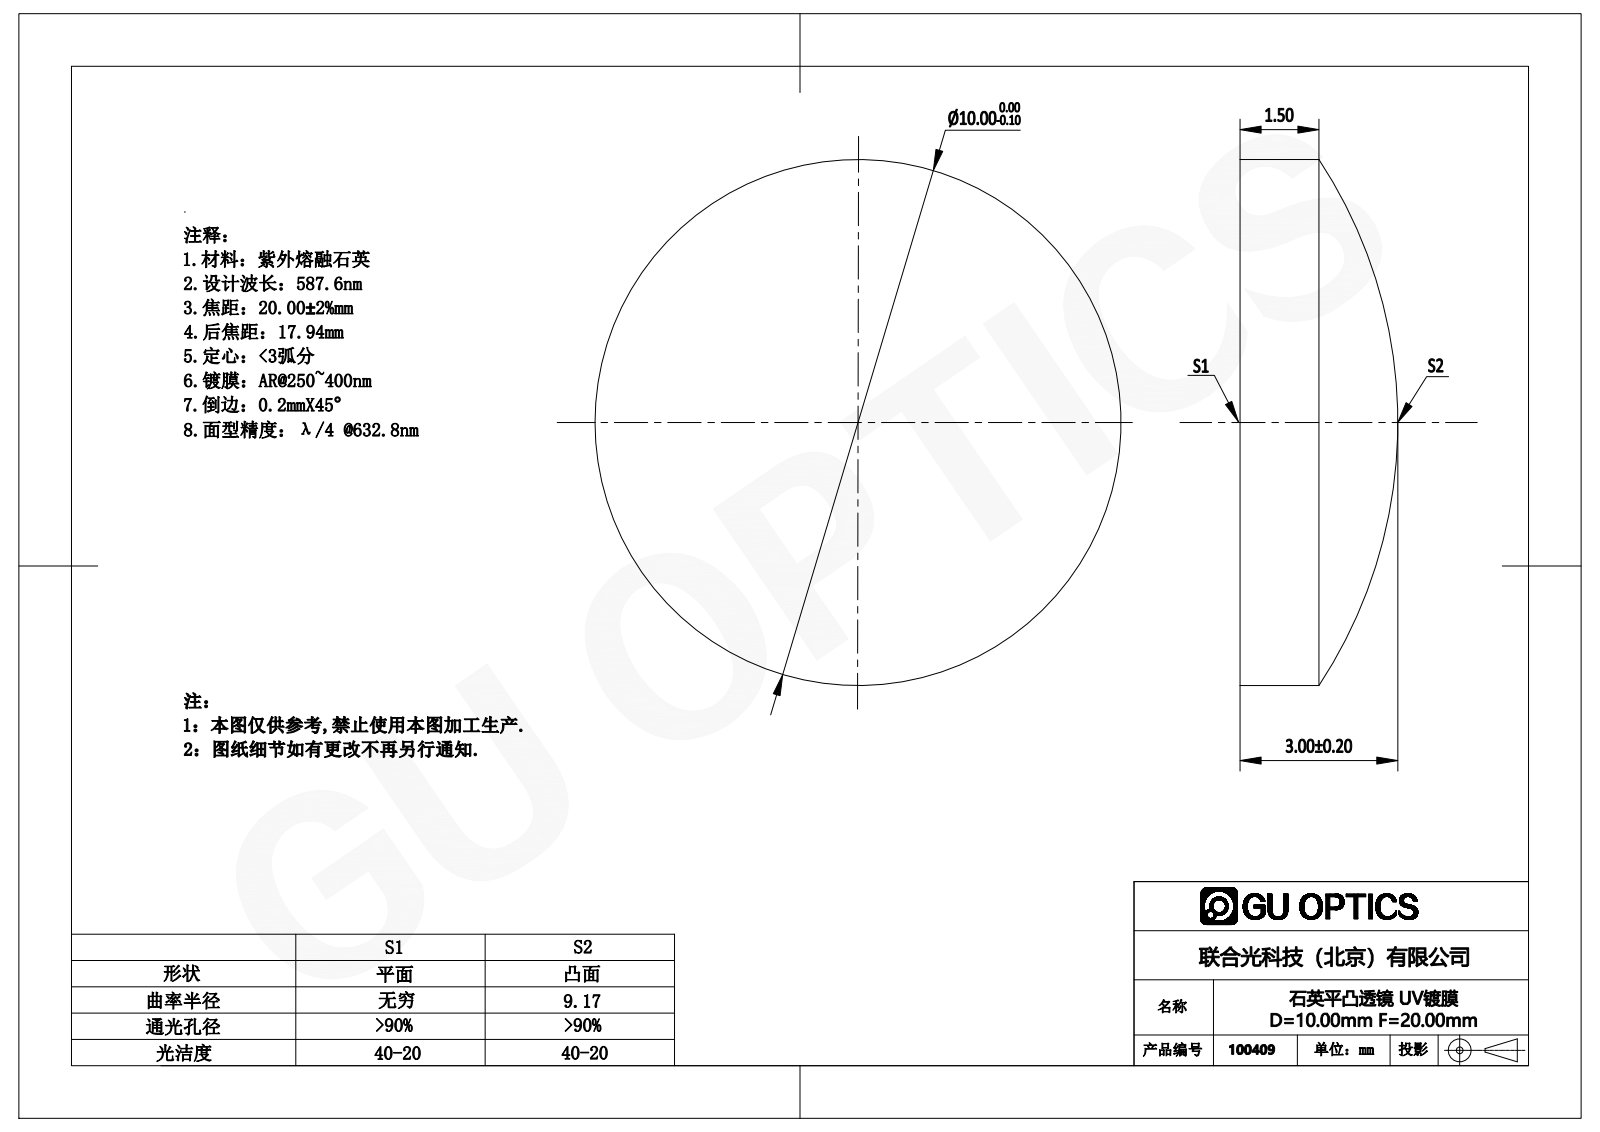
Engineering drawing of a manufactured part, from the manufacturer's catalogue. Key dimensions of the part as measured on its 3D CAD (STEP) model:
Part name (STEP PRODUCT): 100359
STEP written by: SolidWorks 2016 (AUTOMOTIVE_DESIGN)
Units: millimetres
Bodies: 1 solid, 5 faces (1 planar, 2 cylindrical, 2 other)
Overall size (bounding box): 10 × 10 × 3
Volume: 178 mm³ · Surface area: 211 mm²
Round bosses / shafts (diameter × count): ⌀10 ×1
